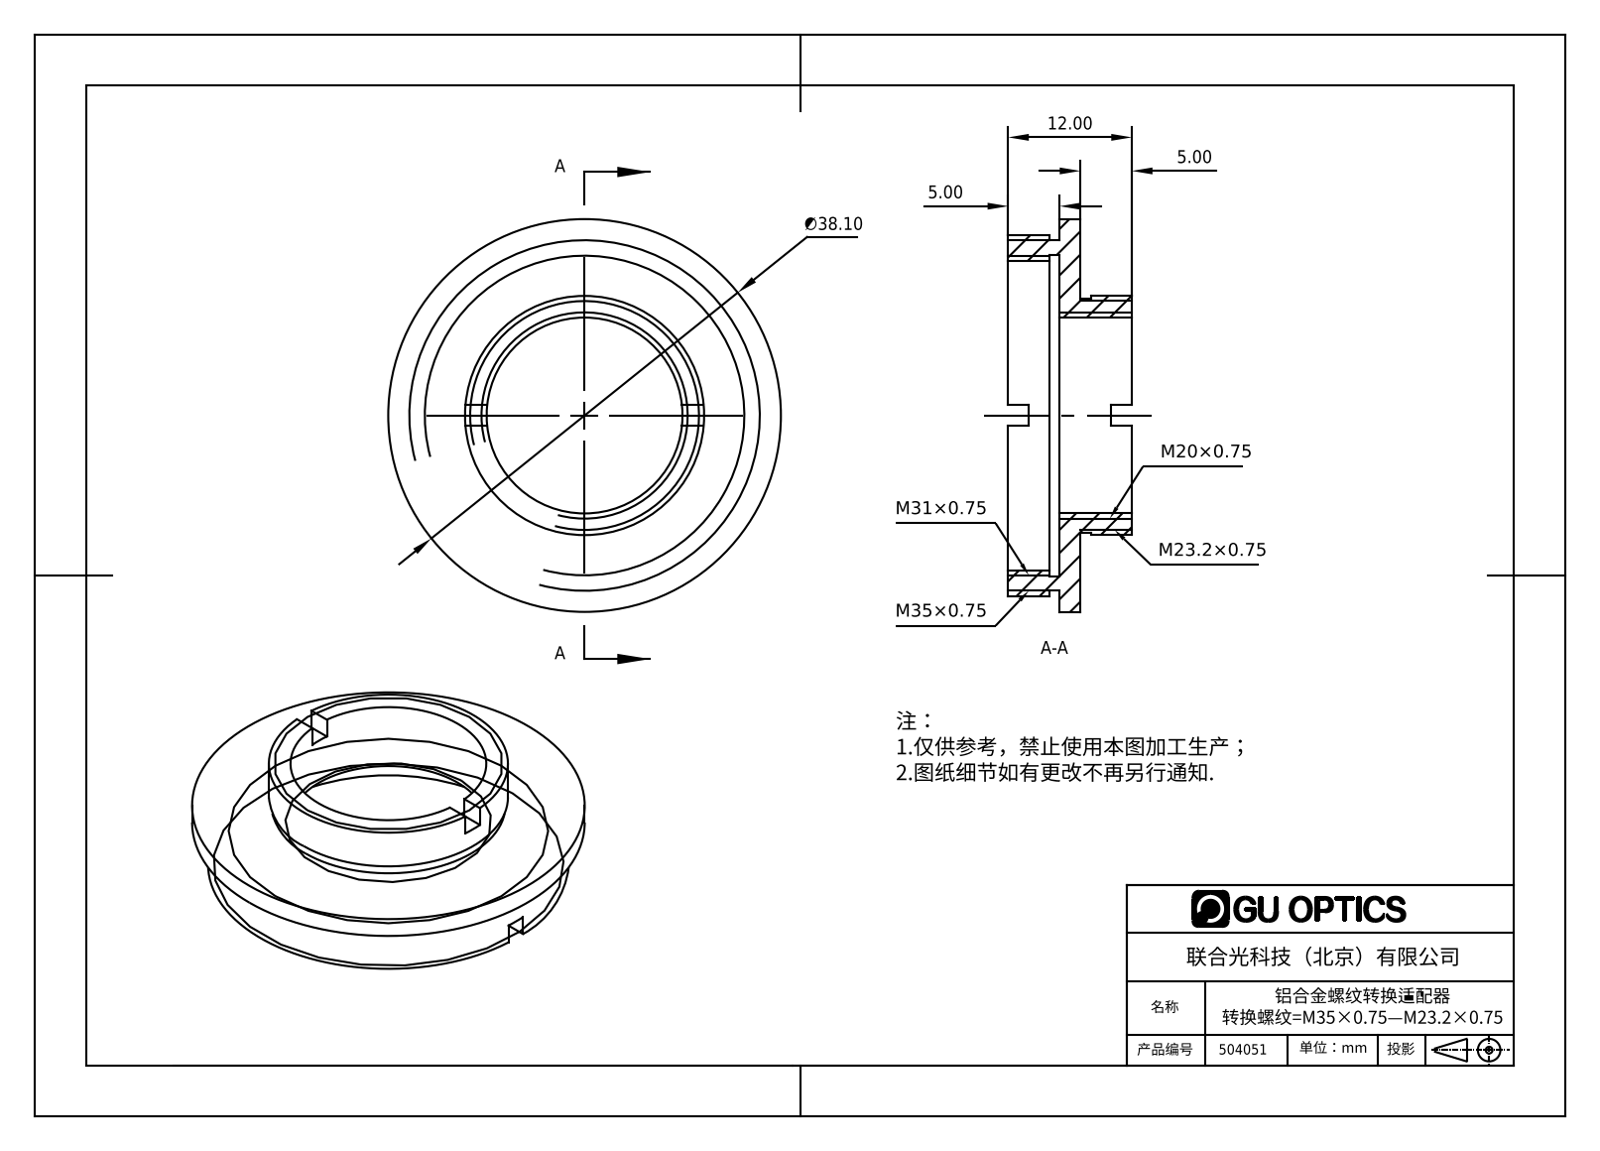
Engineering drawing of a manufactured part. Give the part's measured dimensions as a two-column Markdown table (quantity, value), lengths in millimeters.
| quantity | value |
| --- | --- |
| part name | 504051 |
| STEP written by | SolidWorks 2016 (AUTOMOTIVE_DESIGN) |
| units | millimeters |
| bodies | 1 solid, 38 faces (22 planar, 16 cylindrical, 0 other) |
| overall size | 38.1 × 38.1 × 12 |
| volume | 3 519 mm³ |
| surface area | 4 020 mm² |
| round holes (diameter × count) | 19 × 1, 30 × 1, 31.2 × 1 |
| round bosses / shafts (diameter × count) | 38.1 × 1, 35 × 1, 34 × 1, 23.2 × 1, 22.7 × 1 |
| main face-to-face distances | 2, 5, 7, 3, 4, 8, 12, 1, 10, 6 |
